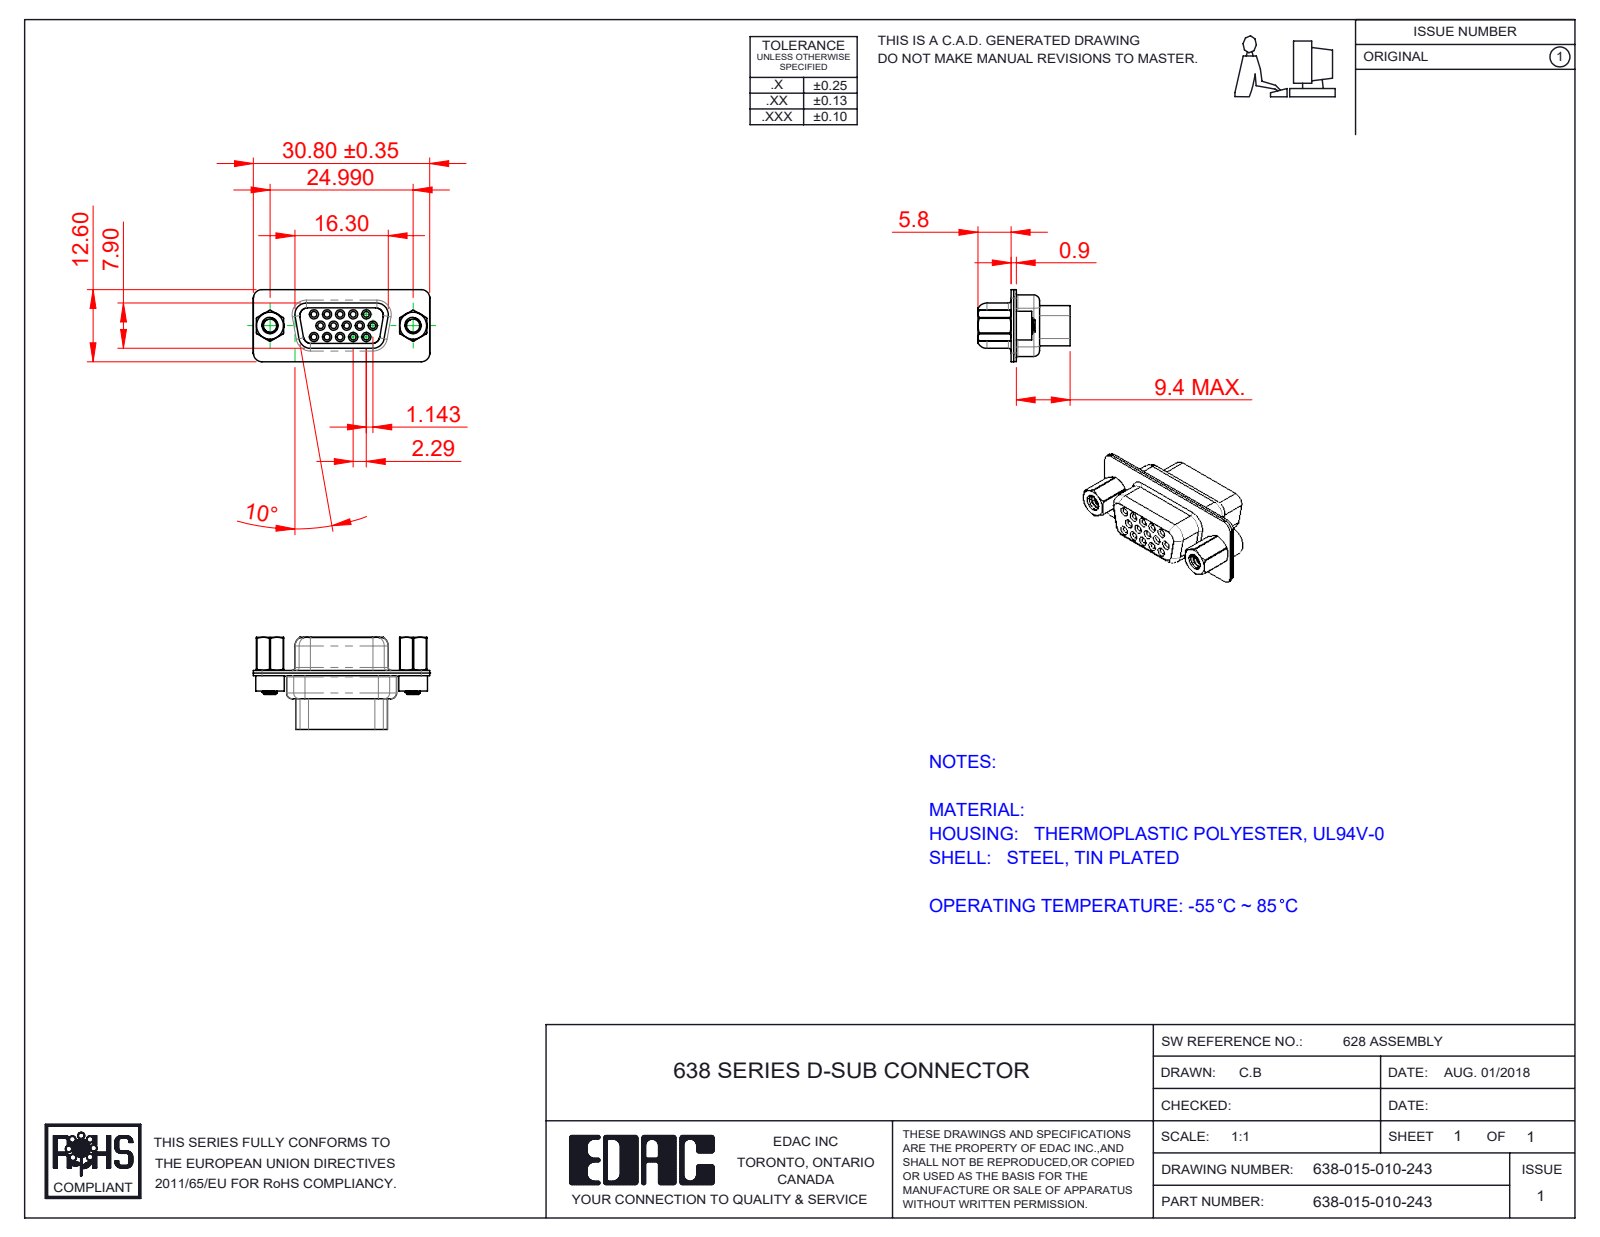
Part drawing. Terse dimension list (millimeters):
name: 638 Shell Rear_15 Contacts; 638-015-010-243; 638 4-40 Hex Standoff; 638 Shell Front_15 Contacts (+2 more)
written by: SolidWorks 2020 (CONFIG_CONTROL_DESIGN)
unit: mm
bodies: 7 solids, 600 faces (134 planar, 329 cylindrical, 137 other)
size: 30.81 × 16.1 × 12.6
volume: 1 924 mm³; area: 5 033 mm²
holes: 15× ⌀1, 15× ⌀1.7, 15× ⌀1.8, 15× ⌀2, 2× ⌀2.26, 2× ⌀2.29, 2× ⌀4, 2× ⌀4.05, 2× ⌀4.85
bosses: 2× ⌀5, 2× ⌀4.95, 2× ⌀4.8, 2× ⌀2.79
rounds: 20× R1.5, 12× R2, 8× R1.55, 5× R1.35, 4× R0.25, 4× R0.5, 4× R0.55, 4× R0.7
face distances: 0.45, 0.9, 0.4, 1.43, 8.88, 6.6, 9.4, 7, 6.7, 5.8
hole spacings: 3.96, 2.28, 4.57, 2.29, 6.05, 6.86, 7.92, 6.04
